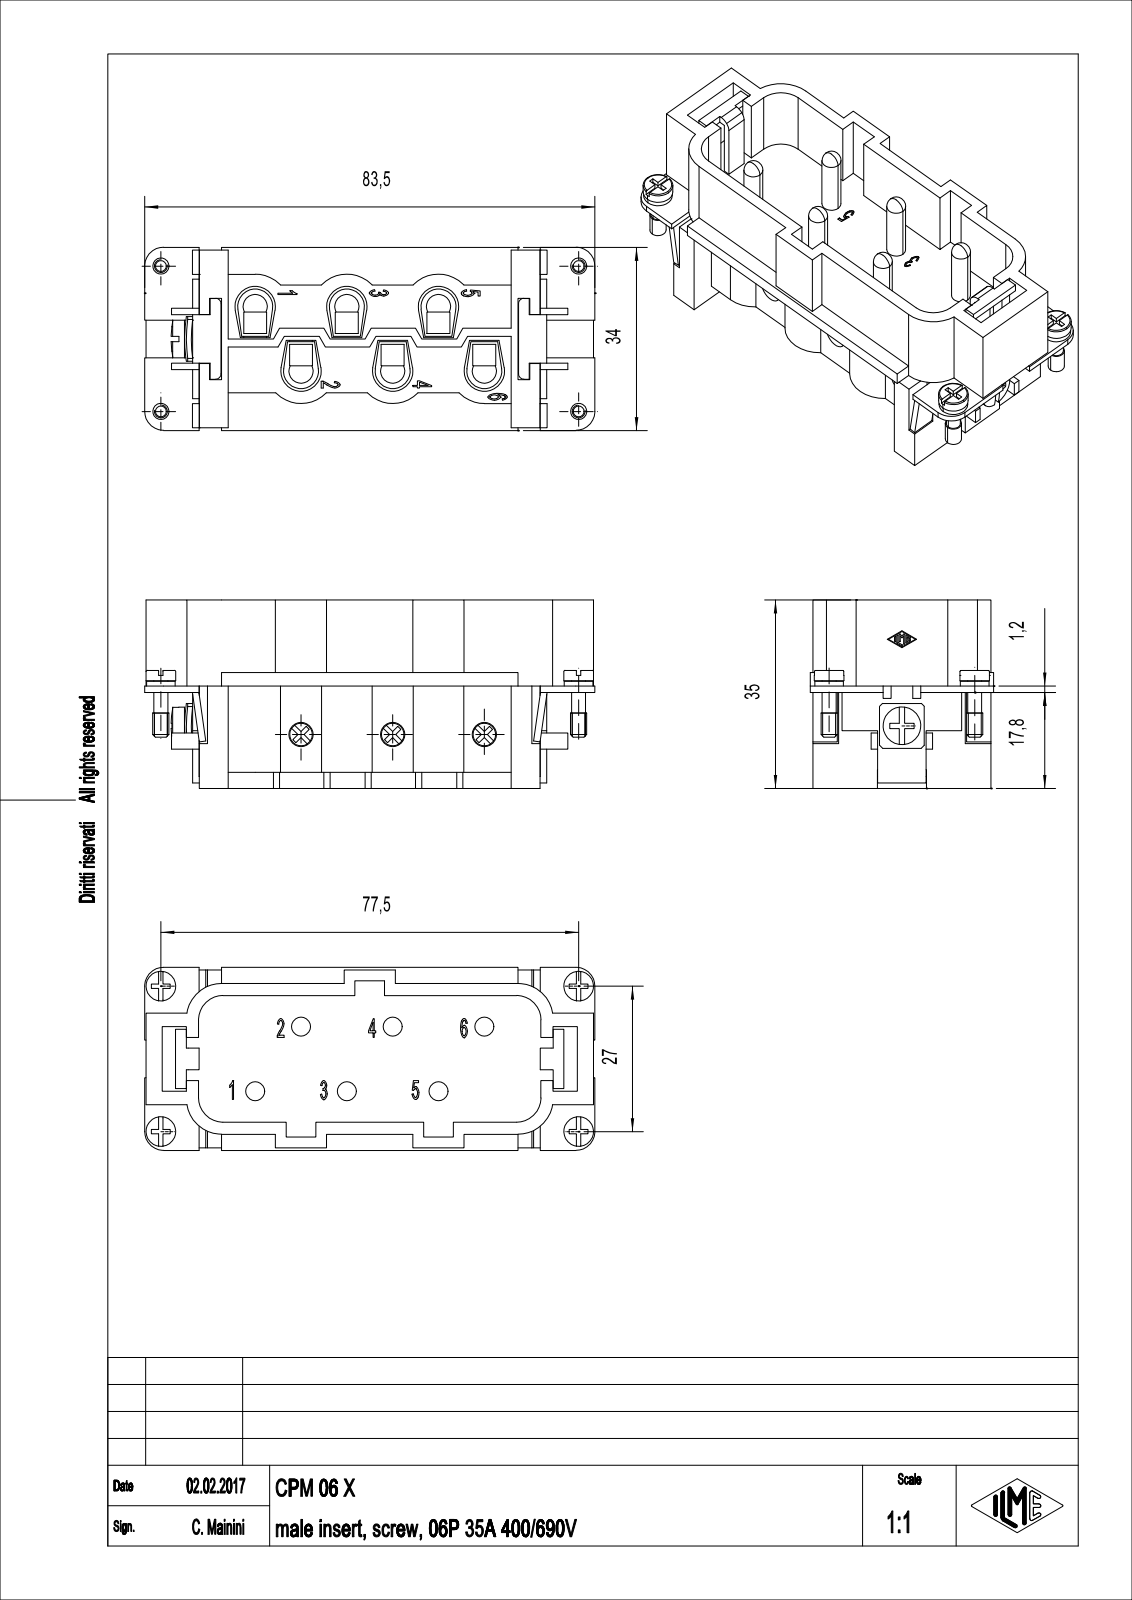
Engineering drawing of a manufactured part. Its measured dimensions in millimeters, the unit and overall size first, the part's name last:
Units: millimetres
Overall size (bounding box): 83.5 × 35 × 34
Round holes (diameter × count): ⌀4.5 ×12, ⌀3.24 ×1
Round bosses / shafts (diameter × count): ⌀4.2 ×6, ⌀3.5 ×6, ⌀5.5 ×4, ⌀5.3 ×4, ⌀3 ×4, ⌀2.6 ×4, ⌀7 ×1
Partial cylindrical surfaces — rounded edges, fillets, slot ends (radius × count): R0.1 ×14, R6.5 ×10, R3.25 ×6, R3.75 ×6, R1 ×4, R3.5 ×4, R4.5 ×4, R2 ×2
Main face-to-face distances: 2.5, 16, 6.5, 18.5, 2.25, 1.2, 8, 4, 25.75, 13.5
Hole centre spacings: 17, 8.5, 14.71, 34, 25.5, 28.18, 42.5, 44.16
Volume: 37 800 mm³ · Surface area: 26 824 mm²
Bodies: 3 solids, 950 faces (644 planar, 166 cylindrical, 140 other)
Part name (STEP PRODUCT): CPM_06_X
STEP written by: PTC Creo Elements/Direct Modeling 19.0E 27-Jun-2016 (C) Parametric Technology GmbH (AUTOMOTIVE_DESIGN)
